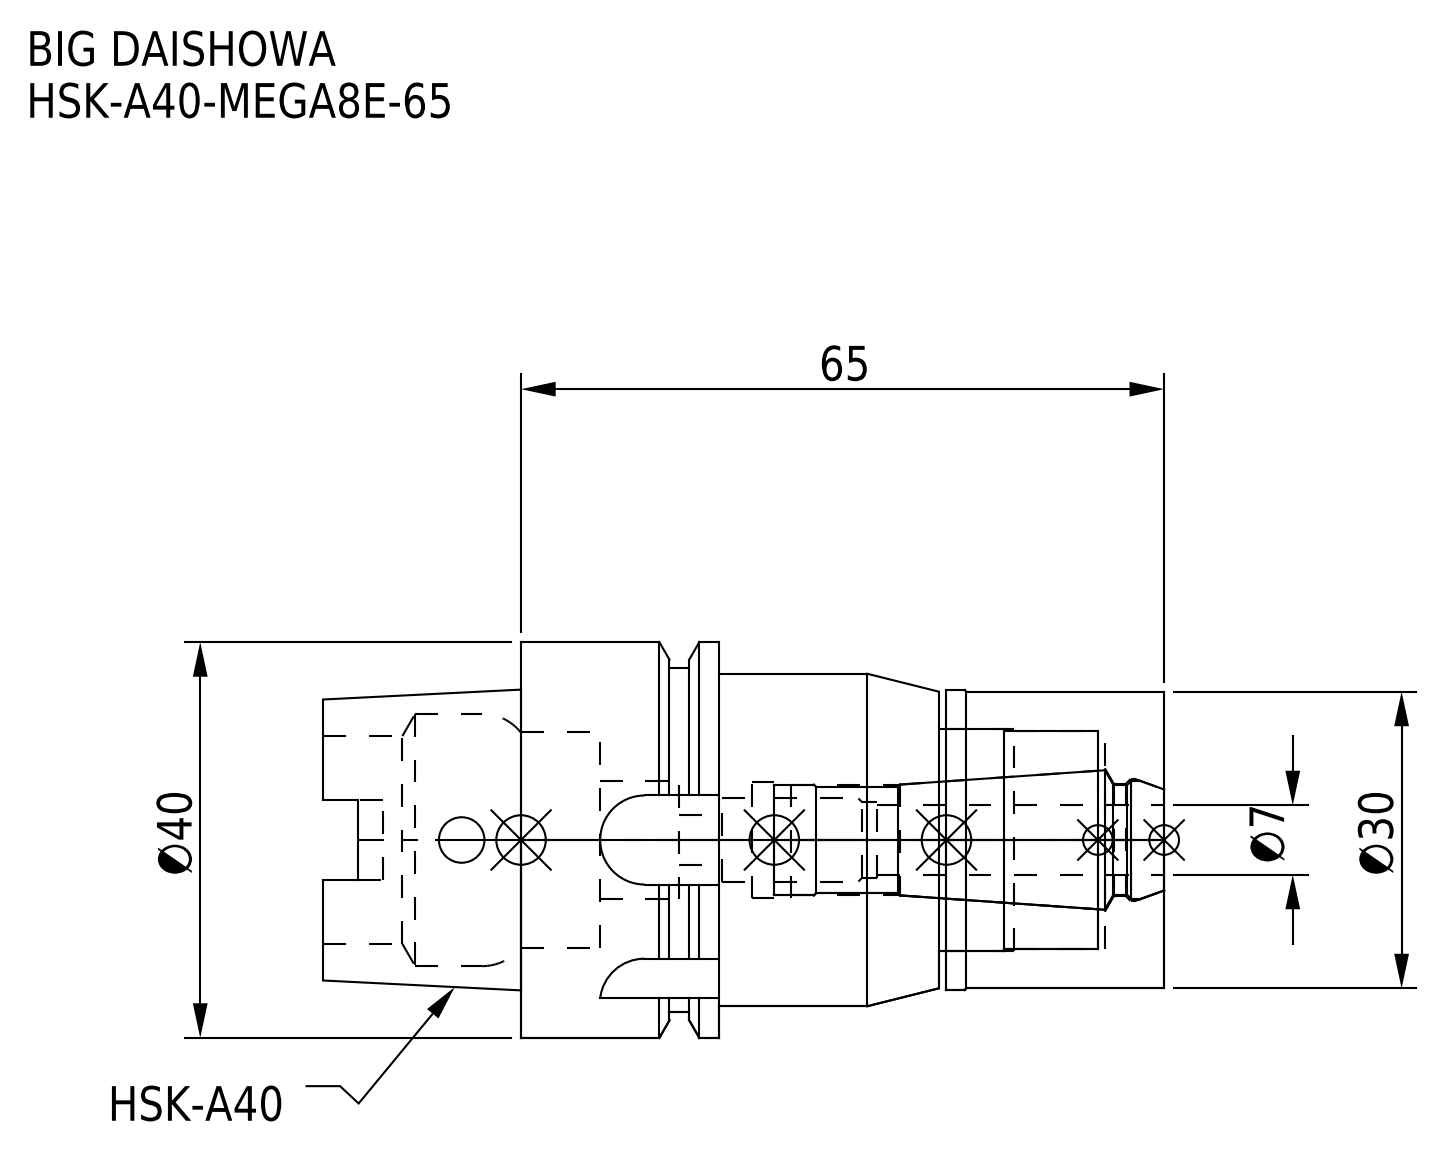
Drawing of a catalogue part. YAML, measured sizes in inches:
part_name: "HSK-A40-MEGA8E-65-080.stp; DXF_TEMP_ASSY_ASM_4_ASM.stp; HSK-A40-MEGA8E-65; HSK-A40-MEGA8E-65_1.stp (+3 more)"
step_written_by: "SolidWorks 2019 (CONFIG_CONTROL_DESIGN)"
units: inches
bodies: {solids: 2, faces: 127, planar: 45, cylindrical: 56, other: 26}
overall_size: [3.346, 1.575, 1.575]
volume: 3.305
surface_area: 29.19
round_holes:
  - {diameter: 0.181, count: 1}
  - {diameter: 0.197, count: 1}
  - {diameter: 0.331, count: 1}
  - {diameter: 0.441, count: 1}
  - {diameter: 0.449, count: 1}
  - {diameter: 0.465, count: 1}
  - {diameter: 0.472, count: 1}
  - {diameter: 0.484, count: 1}
  - {diameter: 0.827, count: 1}
  - {diameter: 0.858, count: 1}
  - {diameter: 0.866, count: 1}
  - {diameter: 0.886, count: 1}
round_bosses_or_shafts:
  - {diameter: 1.575, count: 1}
  - {diameter: 1.37, count: 1}
  - {diameter: 1.323, count: 1}
  - {diameter: 1.193, count: 1}
  - {diameter: 1.181, count: 1}
partial_cylinders:
  - {radius: 0.074, count: 4}
  - {radius: 0.177, count: 4}
face_to_face_distances: [2.559, 0.787, 0.866, 1.693, 0.898, 0.031, 1.661, 1.772, 0.906, 0.874]
